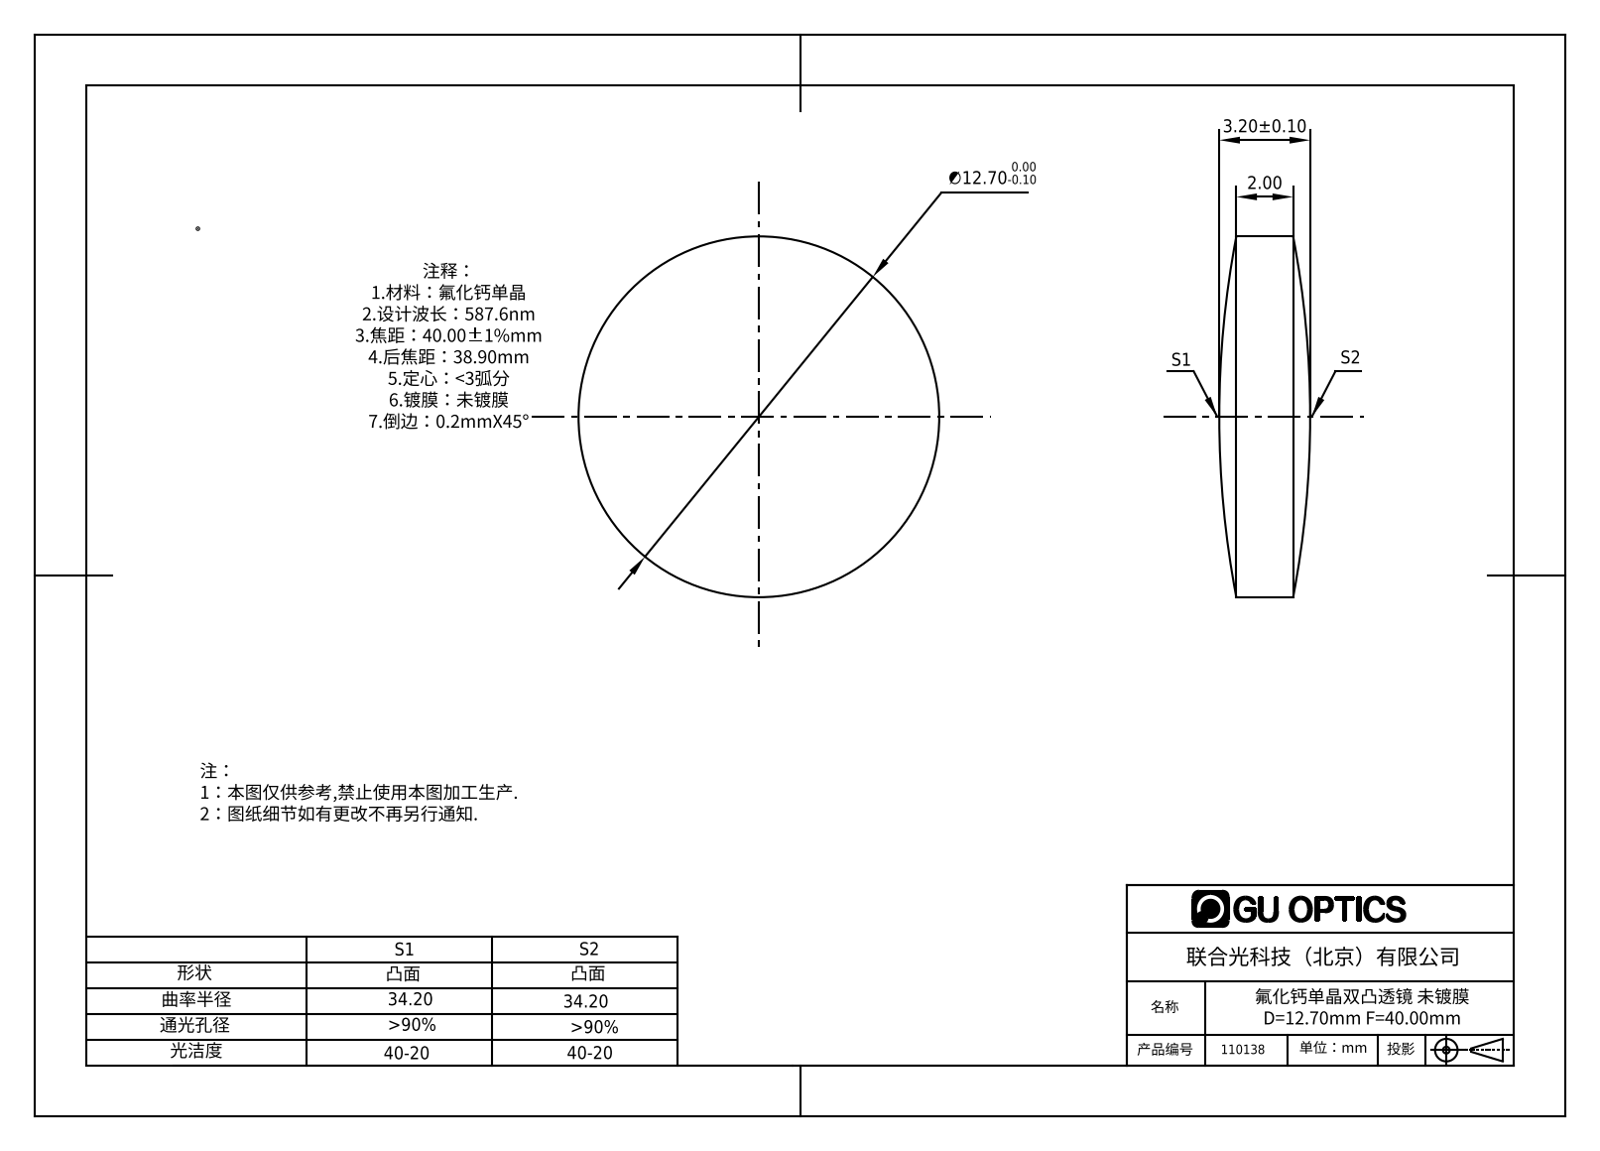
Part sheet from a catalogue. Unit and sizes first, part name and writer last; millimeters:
Units: millimetres
Overall size (bounding box): 12.7 × 12.7 × 3.2
Round bosses / shafts (diameter × count): ⌀12.7 ×1
Volume: 330 mm³ · Surface area: 335 mm²
Bodies: 1 solid, 6 faces (0 planar, 2 cylindrical, 4 other)
Part name (STEP PRODUCT): 110138
STEP written by: SolidWorks 2016 (CONFIG_CONTROL_DESIGN)
